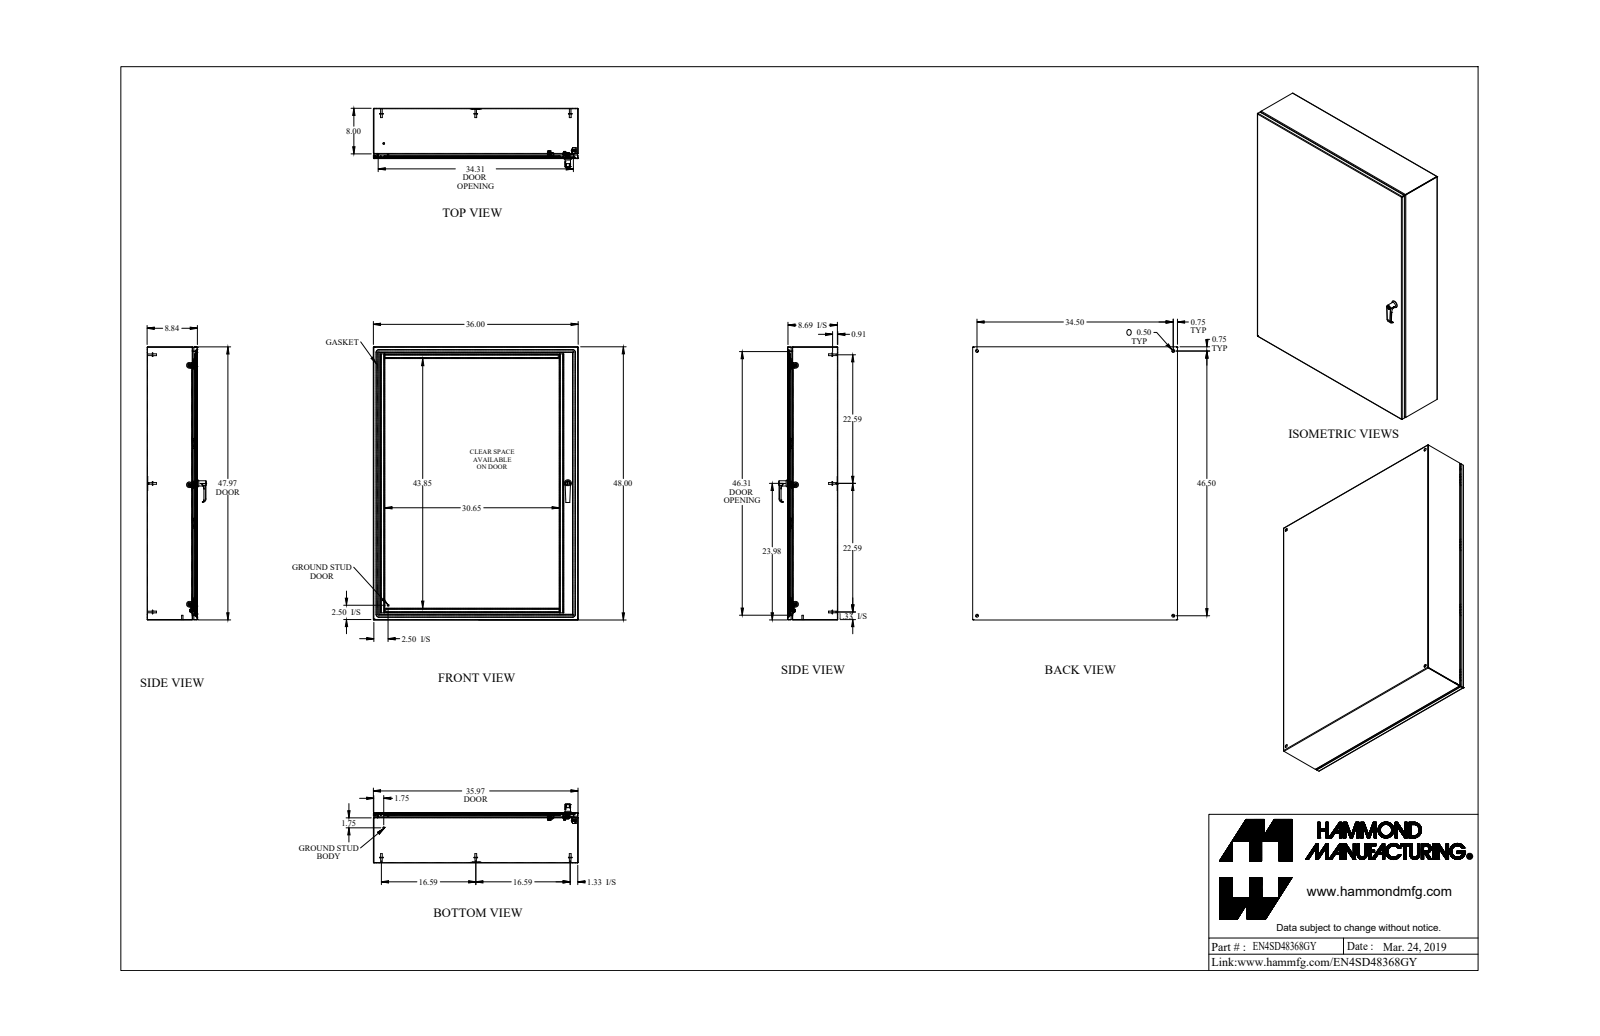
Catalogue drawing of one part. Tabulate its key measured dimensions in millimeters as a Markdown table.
| quantity | value |
| --- | --- |
| part name | EN4SD48368GY_Default |
| STEP written by | SolidWorks 2019 (CONFIG_CONTROL_DESIGN) |
| units | millimeters |
| bodies | 61 solids, 1733 faces (757 planar, 638 cylindrical, 338 other) |
| overall size | 1219.2 × 914.4 × 263.3 |
| volume | 6 665 000 mm³ |
| surface area | 7 341 000 mm² |
| round holes (diameter × count) | 4.5 × 6, 5 × 4, 12.7 × 4, 6.4 × 3, 6.7 × 3, 10.5 × 3, 6.5 × 2, 8 × 2, 10 × 2, 4.4 × 1, 6.1 × 1, 6.1 × 1 |
| round bosses / shafts (diameter × count) | 15.9 × 9, 8 × 8, 6.9 × 8, 6.4 × 8, 9.5 × 6, 4 × 6, 25.4 × 3, 16 × 2 |
| partial cylindrical surfaces (radius × count) | 1.1 × 24, 2.1 × 24, 1.6 × 21, 0.9 × 20, 2.7 × 20, 0.8 × 15, 2.4 × 10, 0.4 × 9 |
| main face-to-face distances | 1.8, 222.6, 220.8, 224.5, 912.6, 1217.4, 910.7, 914.4, 1215.5, 1219.2 |
| hole center spacings | 20, 532.9, 1066, 63.7, 533.1, 533.4, 851, 876.3 |
